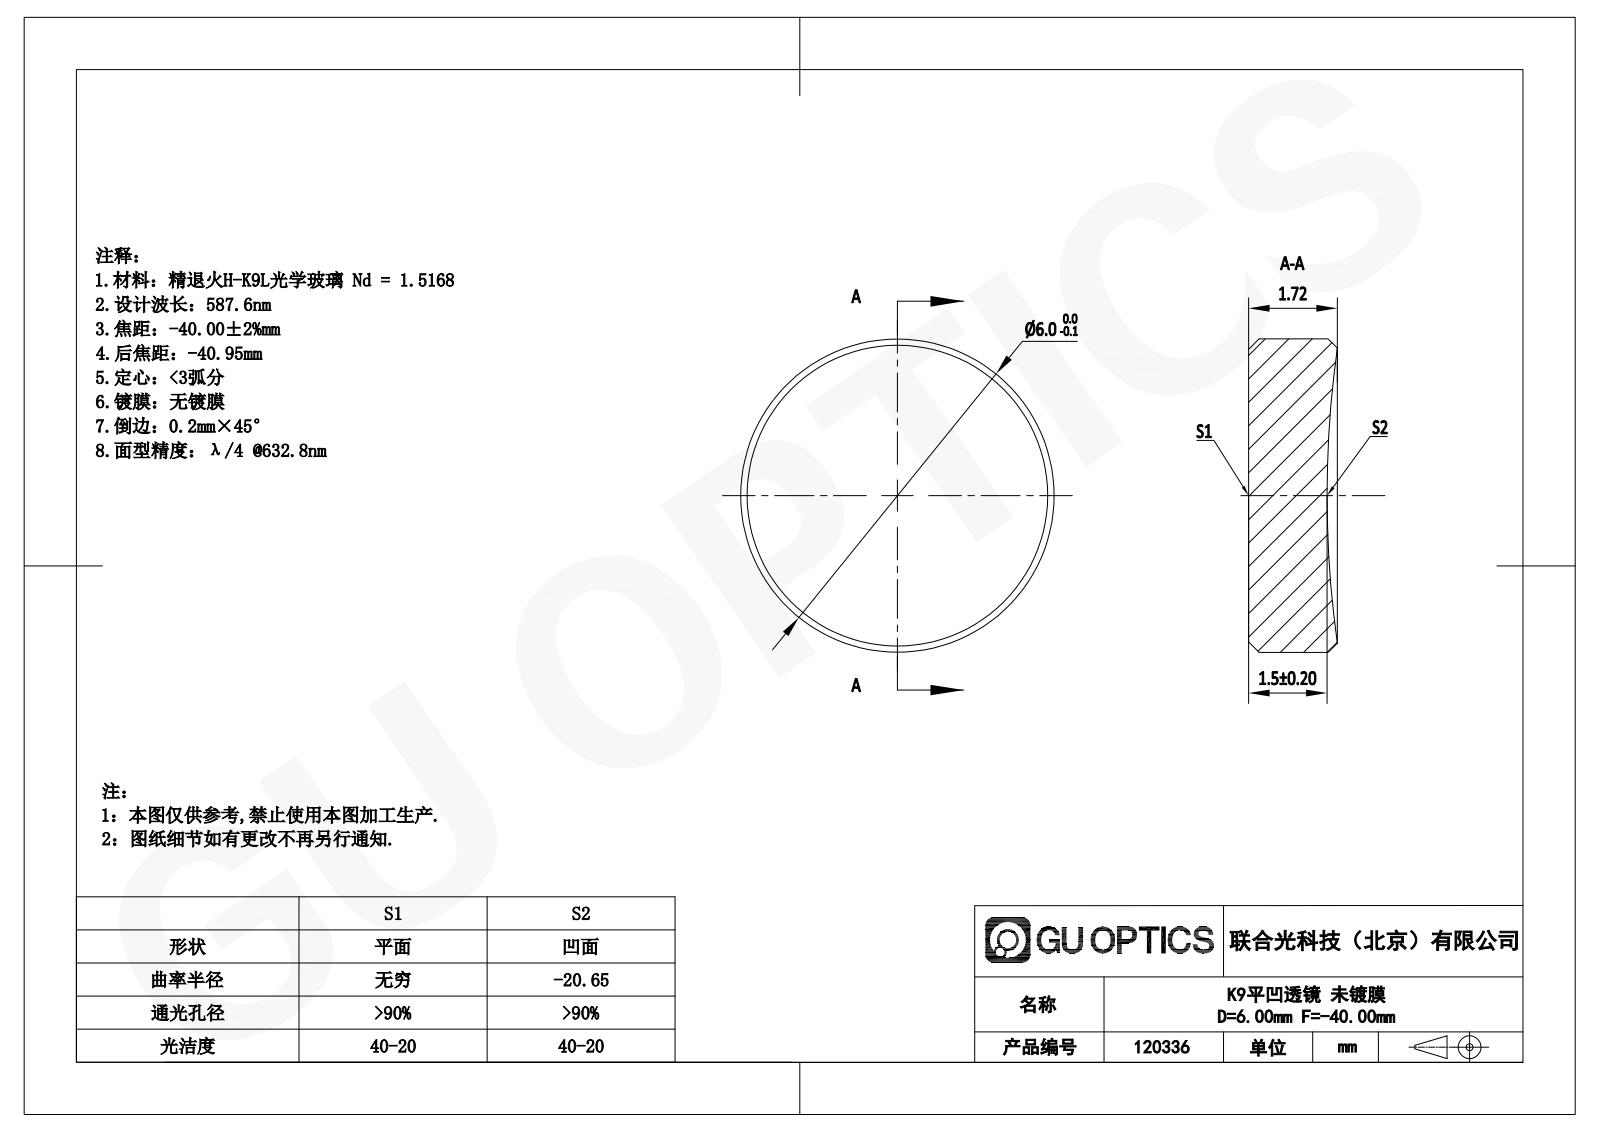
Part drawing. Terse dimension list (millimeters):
name: GL13-006A-040
written by: SolidWorks 2022 (AUTOMOTIVE_DESIGN)
unit: mm
bodies: 1 solid, 9 faces (1 planar, 2 cylindrical, 6 other)
size: 6 × 6 × 1.7
volume: 45 mm³; area: 84 mm²
bosses: 1× ⌀6
